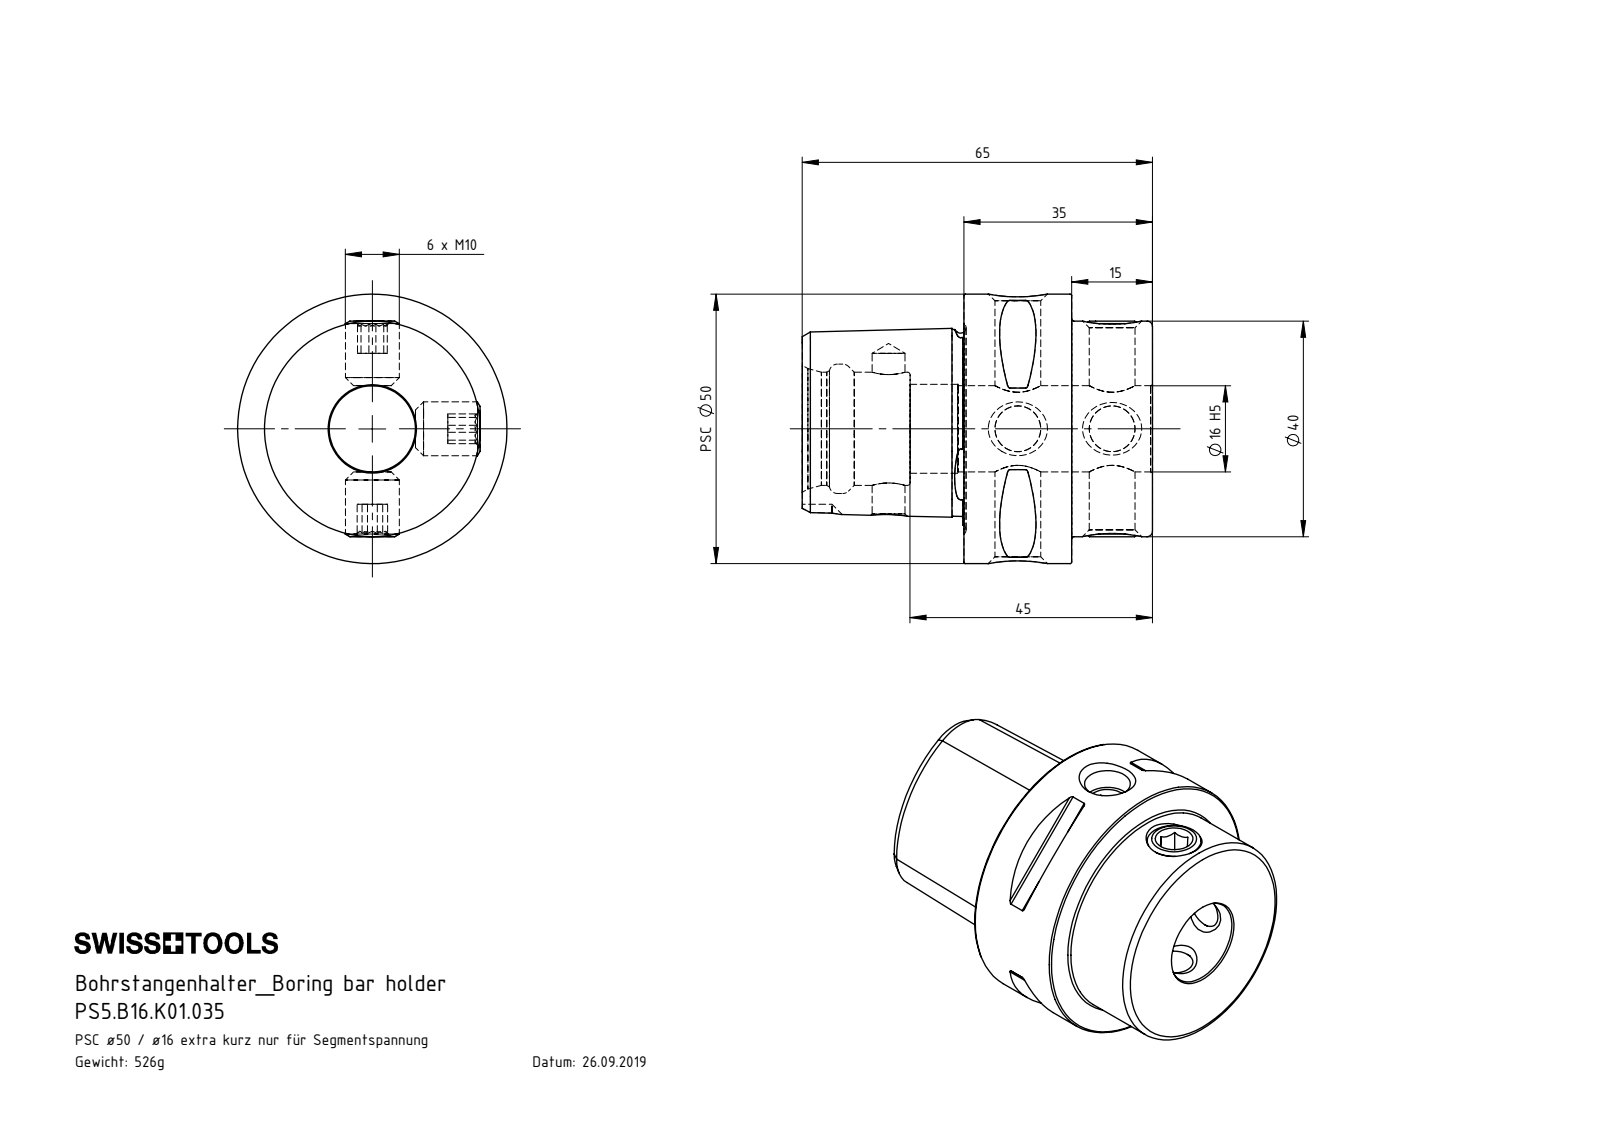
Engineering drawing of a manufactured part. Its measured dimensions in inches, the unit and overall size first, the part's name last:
Units: inches
Overall size (bounding box): 2.559 × 1.969 × 1.969
Round holes (diameter × count): ⌀0.335 ×4, ⌀0.24 ×1, ⌀0.63 ×1, ⌀0.65 ×1, ⌀0.827 ×1, ⌀0.945 ×1
Round bosses / shafts (diameter × count): ⌀0.394 ×4, ⌀1.969 ×1, ⌀1.575 ×1
Partial cylindrical surfaces — rounded edges, fillets, slot ends (radius × count): R0.02 ×8, R0.157 ×1
Main face-to-face distances: 1.378, 0.787, 0.591, 1.181, 1.969, 2.559, 0.197, 0.236, 0.755, 1.748
Hole centre spacings: 0.689, 0.945, 1.634
Volume: 4.092 in³ · Surface area: 32 in²
Bodies: 7 solids, 177 faces (74 planar, 30 cylindrical, 73 other)
Part name (STEP PRODUCT): PS5-B16.K01.035_A; PS5.B16.K01.035; ISO 4026 - M10 x 12_PreviewCfg
STEP written by: SolidWorks 2017 (AUTOMOTIVE_DESIGN)
